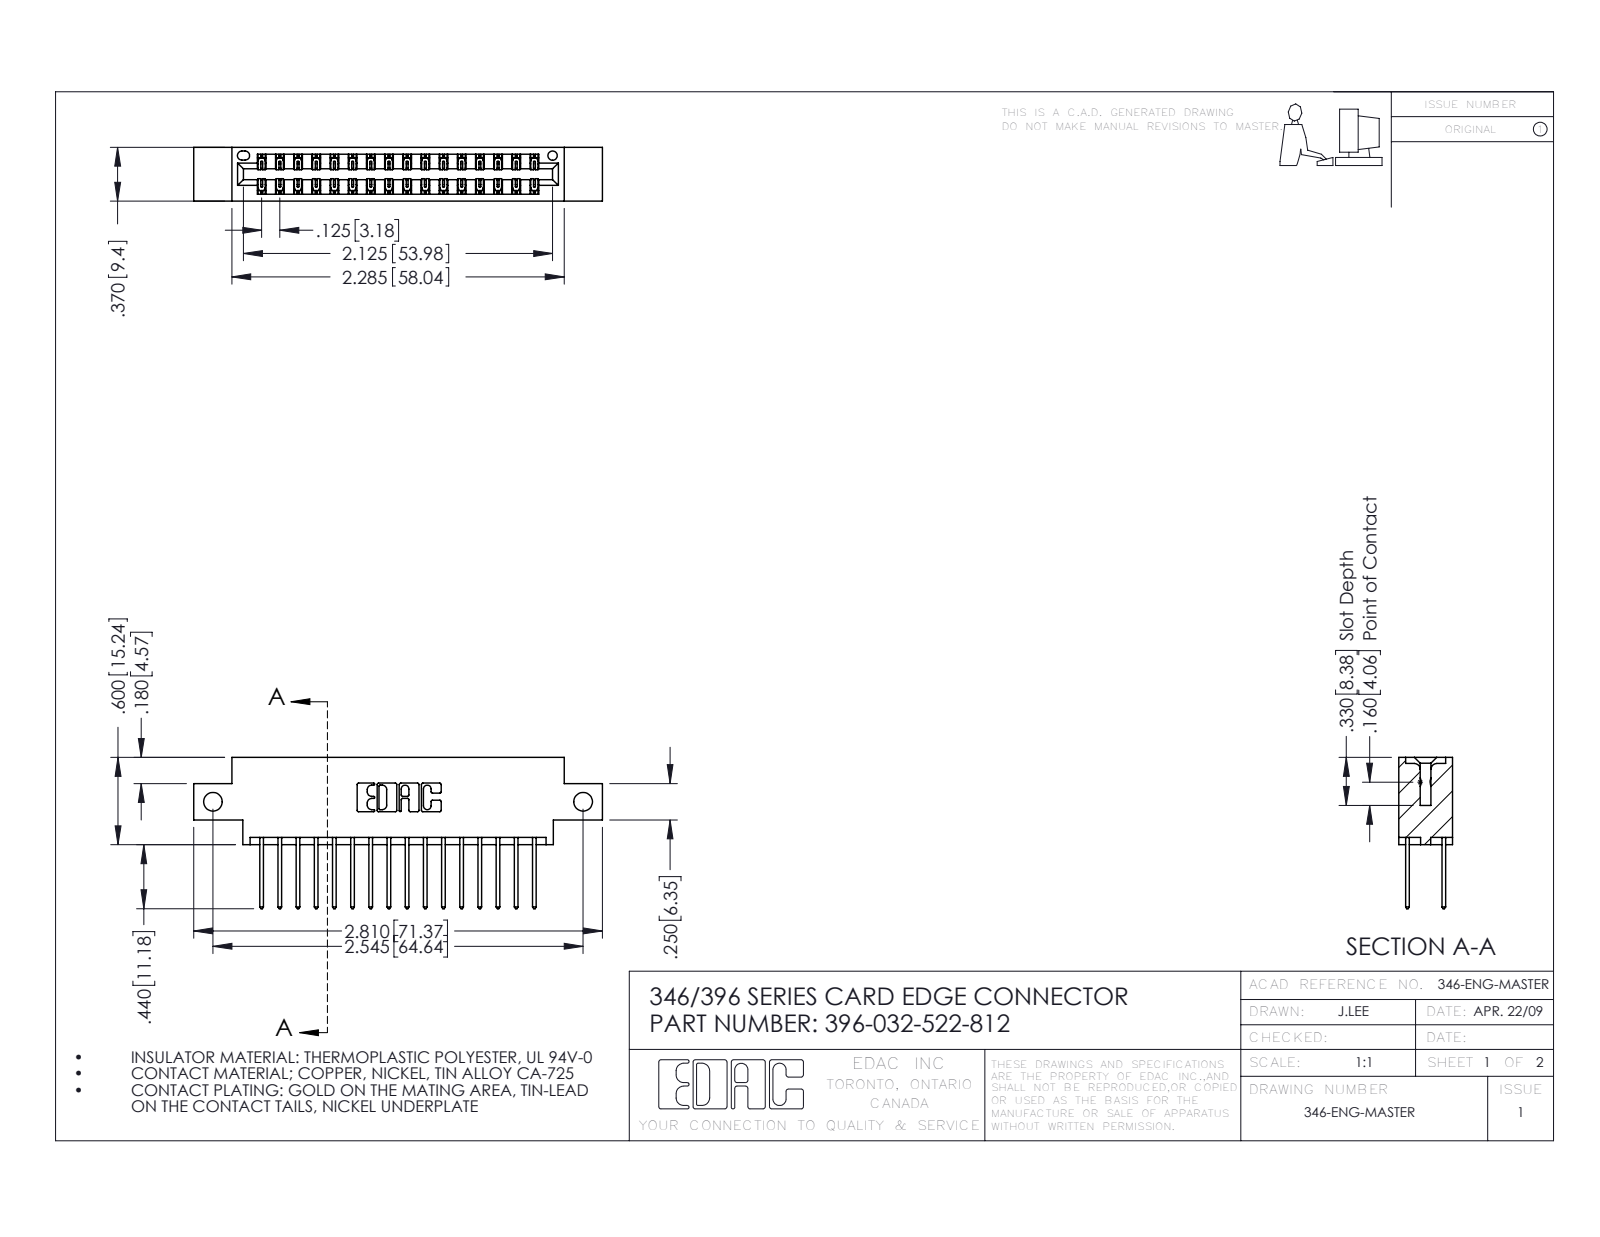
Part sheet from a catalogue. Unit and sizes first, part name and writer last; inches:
Units: inches
Overall size (bounding box): 2.81 × 1.04 × 0.37
Round holes (diameter × count): ⌀0.128 ×2, ⌀0.064 ×1
Partial cylindrical surfaces — rounded edges, fillets, slot ends (radius × count): R0.006 ×48, R0.01 ×32, R0.01 ×22, R0.007 ×6, R0.031 ×6, R0.026 ×3, R0.014 ×2, R0.022 ×2
Main face-to-face distances: 0.048, 0.322, 0.25, 0.37, 0.072, 0.298, 0.025, 0.275, 0.148, 0.222
Hole centre spacings: 2.545
Volume: 0.403 in³ · Surface area: 14.08 in²
Bodies: 33 solids, 1790 faces (1200 planar, 590 cylindrical, 0 other)
Part name (STEP PRODUCT): 396-032-522-812; 346 Part_0.170 Offset - Side Mount; 345-292-001_345-293-122
STEP written by: SolidWorks 2016 (CONFIG_CONTROL_DESIGN)
